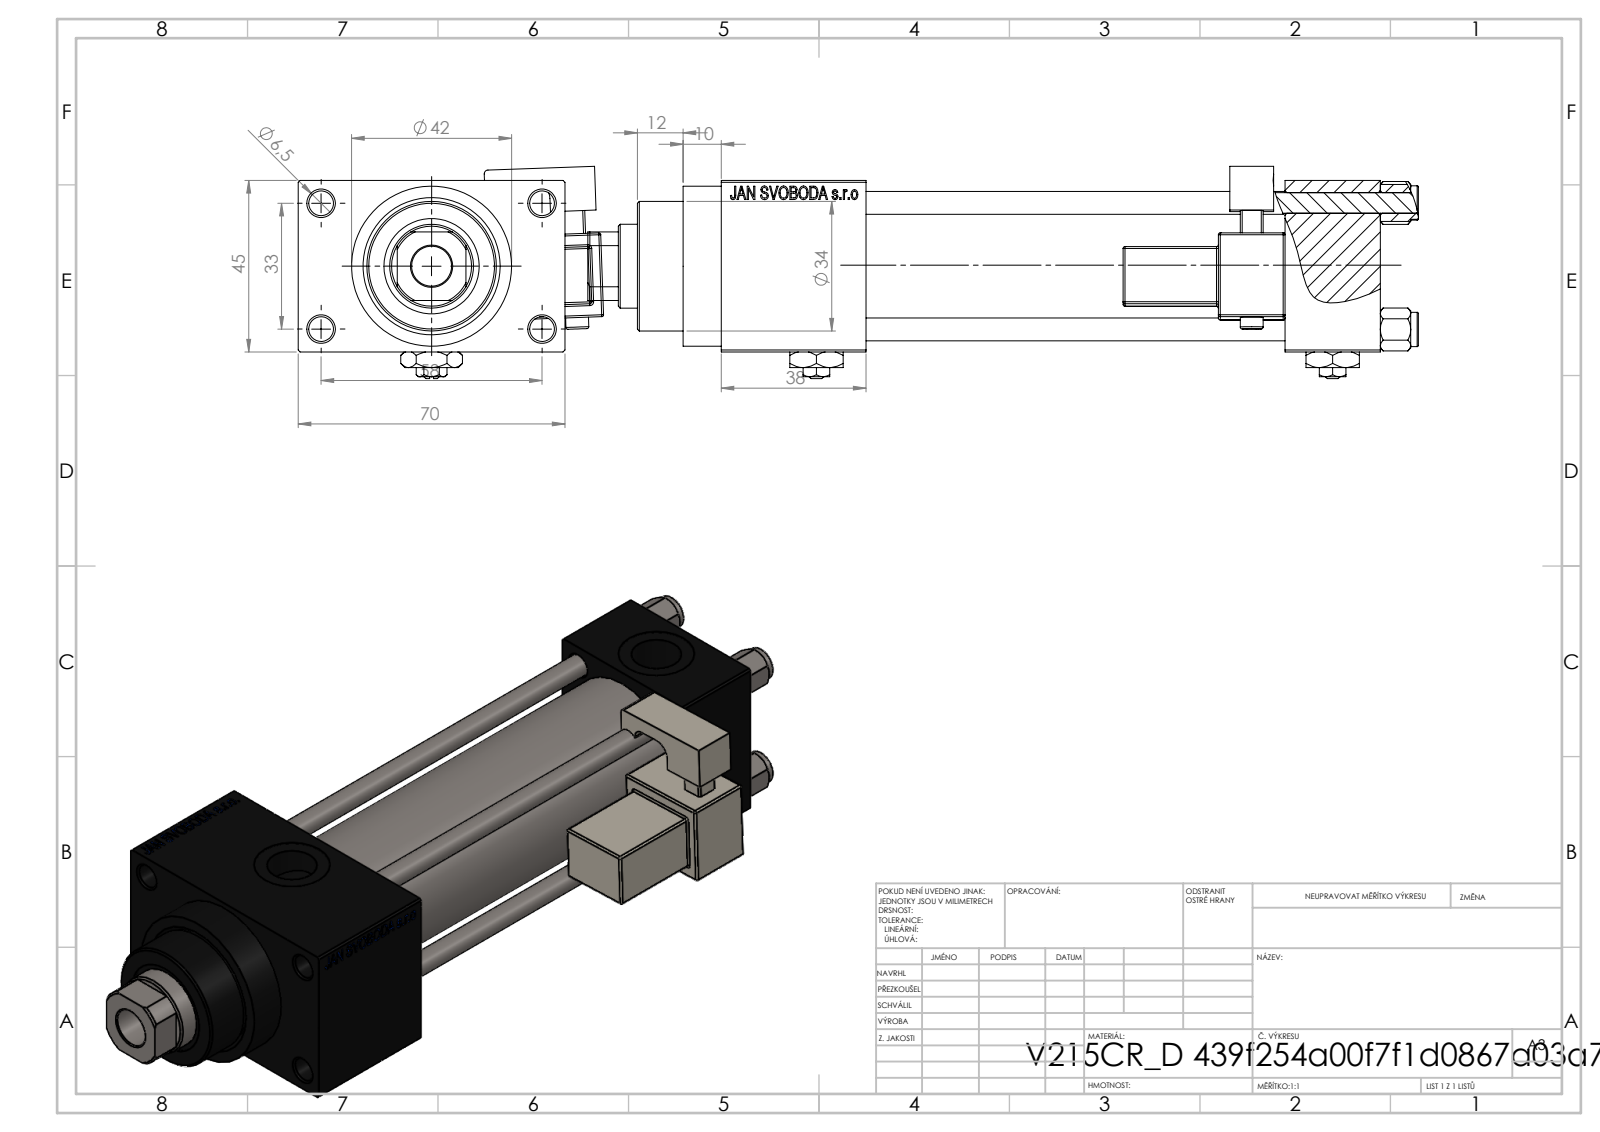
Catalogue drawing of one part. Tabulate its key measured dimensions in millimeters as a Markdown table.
| quantity | value |
| --- | --- |
| part name | V215CR_D_TYCINKA; V215CR_VCP_D; Zatka_pro_OIL_PORT; V215_VC_A (+3 more) |
| STEP written by | SolidWorks 2019 (CONFIG_CONTROL_DESIGN) |
| units | millimeters |
| bodies | 14 solids, 1283 faces (573 planar, 130 cylindrical, 580 other) |
| overall size | 218 × 80.15 × 55.72 |
| volume | 312 962 mm³ |
| surface area | 108 978 mm² |
| round holes (diameter × count) | 6 × 4, 6.5 × 4, 7 × 2, 13.16 × 2, 20 × 2, 10.5 × 1, 22 × 1, 24 × 1, 25 × 1, 32 × 1, 33 × 1 |
| round bosses / shafts (diameter × count) | 9 × 4, 42 × 1, 38 × 1, 34 × 1, 6 × 1 |
| partial cylindrical surfaces (radius × count) | 0.5 × 24, 1 × 1, 2.5 × 1, 4 × 1, 10.5 × 1 |
| main face-to-face distances | 45, 12.5, 25, 57.5, 110, 135, 38, 148, 70, 173 |
| hole center spacings | 12.4, 23.48, 33.2, 33.37, 35.35, 45.6, 56.35, 33 |
